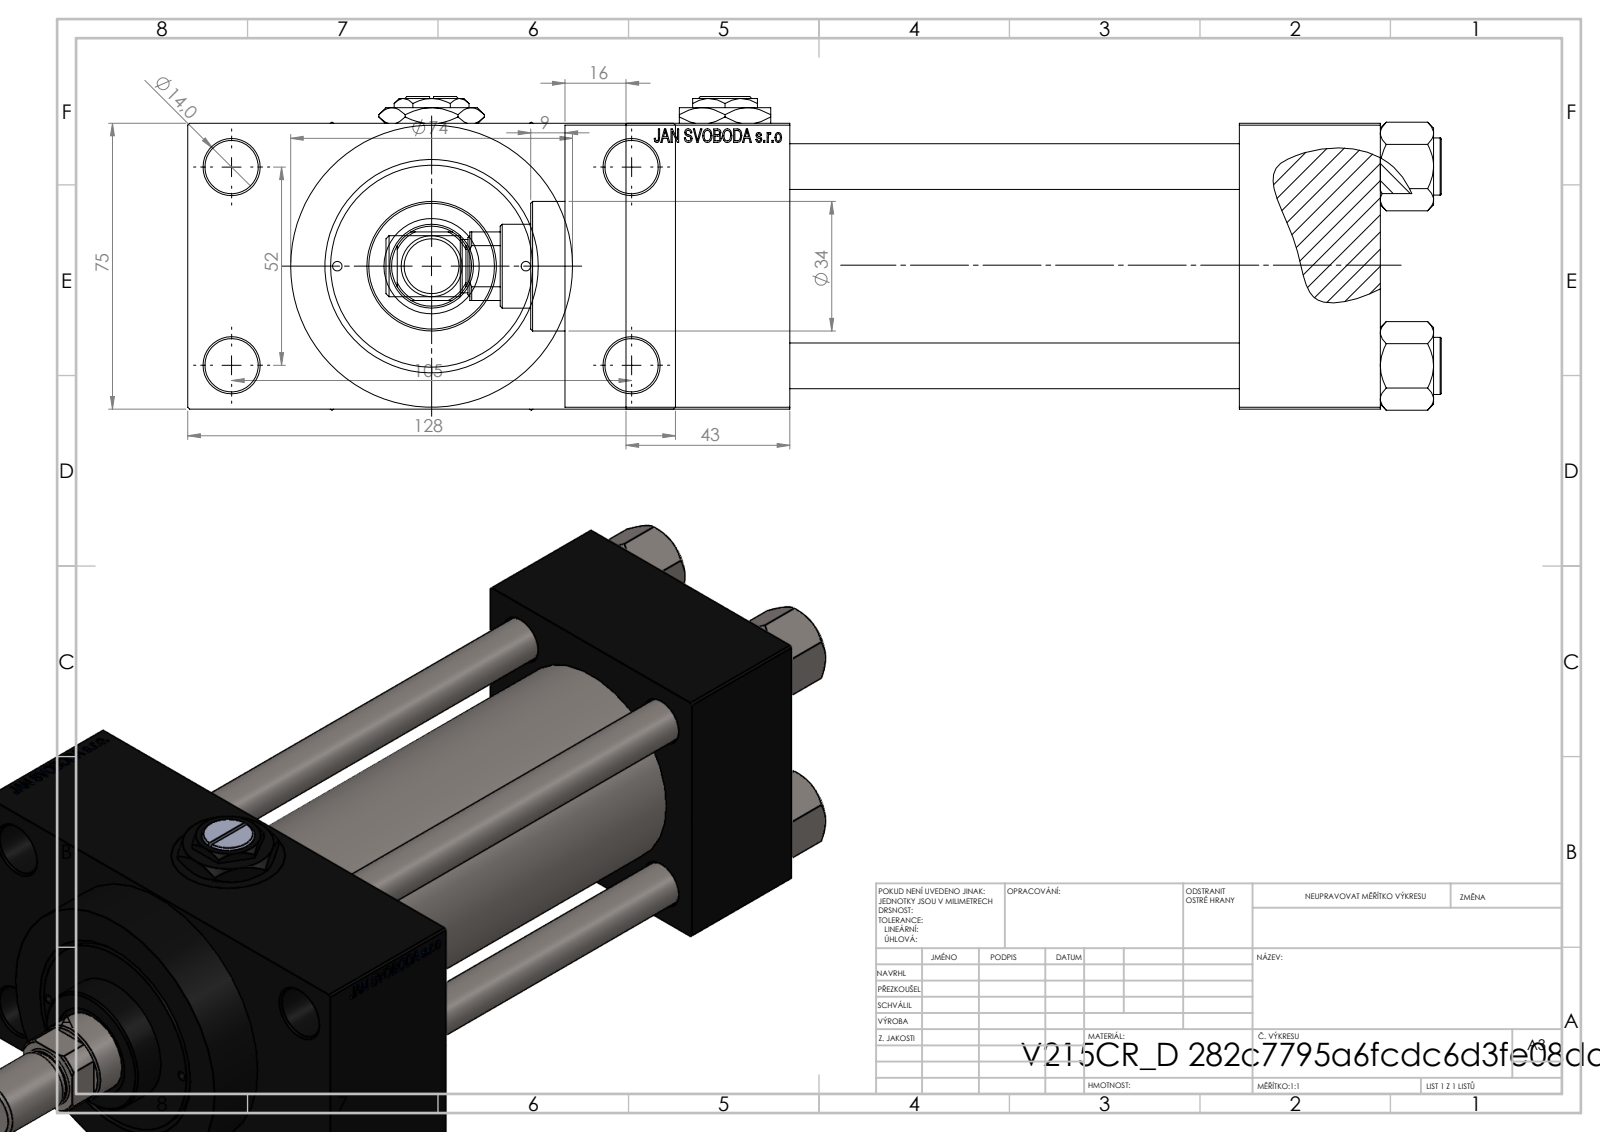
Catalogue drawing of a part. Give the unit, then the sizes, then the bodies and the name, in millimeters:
Units: millimetres
Overall size (bounding box): 277 × 128 × 82.27
Round holes (diameter × count): ⌀12 ×4, ⌀14 ×4, ⌀20.96 ×3, ⌀30 ×3, ⌀2.5 ×2, ⌀7 ×2, ⌀10.5 ×1, ⌀22 ×1, ⌀25 ×1, ⌀41 ×1, ⌀50 ×1, ⌀53 ×1
Round bosses / shafts (diameter × count): ⌀15 ×4, ⌀74 ×1, ⌀56 ×1, ⌀34 ×1, ⌀16 ×1, ⌀14 ×1
Partial cylindrical surfaces — rounded edges, fillets, slot ends (radius × count): R10.5 ×1
Main face-to-face distances: 75, 118, 37, 155, 26.5, 198, 161, 43, 101.5, 16
Hole centre spacings: 26.19, 26.35, 36.98, 38.03, 52.3, 57.22, 58.43, 58.59
Volume: 879 296 mm³ · Surface area: 202 966 mm²
Bodies: 13 solids, 1173 faces (527 planar, 100 cylindrical, 546 other)
Part name (STEP PRODUCT): V215CR_D_TYCINKA; V215CR_VCP_D; NUT_M5_D; ROD_END_AH (+3 more)
STEP written by: SolidWorks 2019 (CONFIG_CONTROL_DESIGN)
